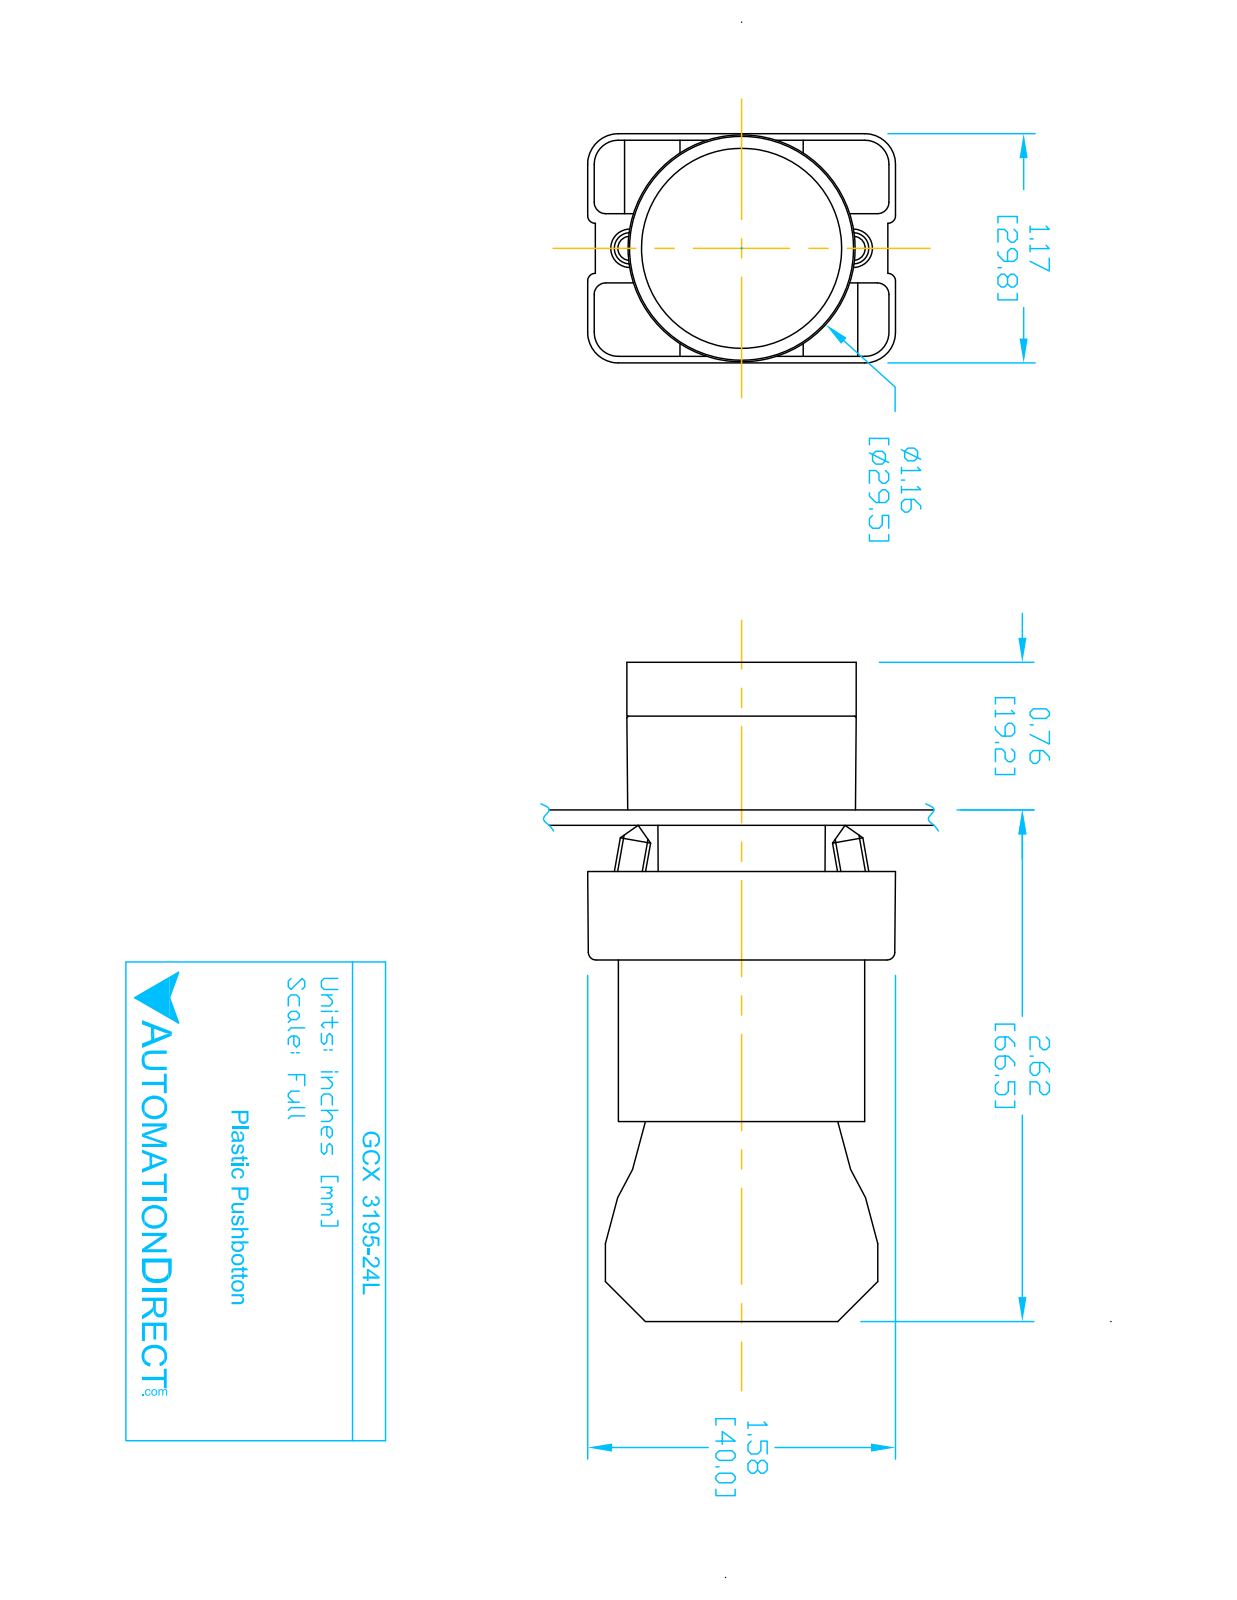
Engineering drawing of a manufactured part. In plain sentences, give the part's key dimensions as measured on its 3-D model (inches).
The part is named "CONTACT BLOCK; ECX3029-2; GCX3195-24L; GCX3195L OPERATOR (+1 more)". Its 3-D file was written by "SolidWorks 2016 (AUTOMOTIVE_DESIGN)". It is 8 solids with 431 faces: 252 planar, 148 cylindrical and 31 other. Overall it measures 3.319 by 1.581 by 1.177 inches. Its volume is 2.794 cubic inches and its surface area 38.77 square inches. Round holes: 2 of diameter 0.079, 2 of diameter 0.124, 2 of diameter 0.13, 1 of diameter 0.087, 1 of diameter 0.197, 1 of diameter 0.469, 1 of diameter 0.878, 1 of diameter 0.888, 1 of diameter 1.024. Round bosses or shafts: 4 of diameter 0.157, 1 of diameter 1.175, 1 of diameter 1.004, 1 of diameter 0.945, 1 of diameter 0.856, 1 of diameter 0.78, 1 of diameter 0.504. Partial cylindrical surfaces (rounded edges, fillets, slot ends): 24 of radius 0.059, 12 of radius 0.041, 12 of radius 0.124, 12 of radius 0.157, 8 of radius 0.039, 2 of radius 0.128, 1 of radius 0.02, 1 of radius 0.063. The main face-to-face distances are 0.827, 0.579, 2.02, 1.193, 1.171, 0.276, 2.295, 1.469, 0.031, 0.033. The hole center spacings are 0.236, 0.544, 0.472, 0.49.
